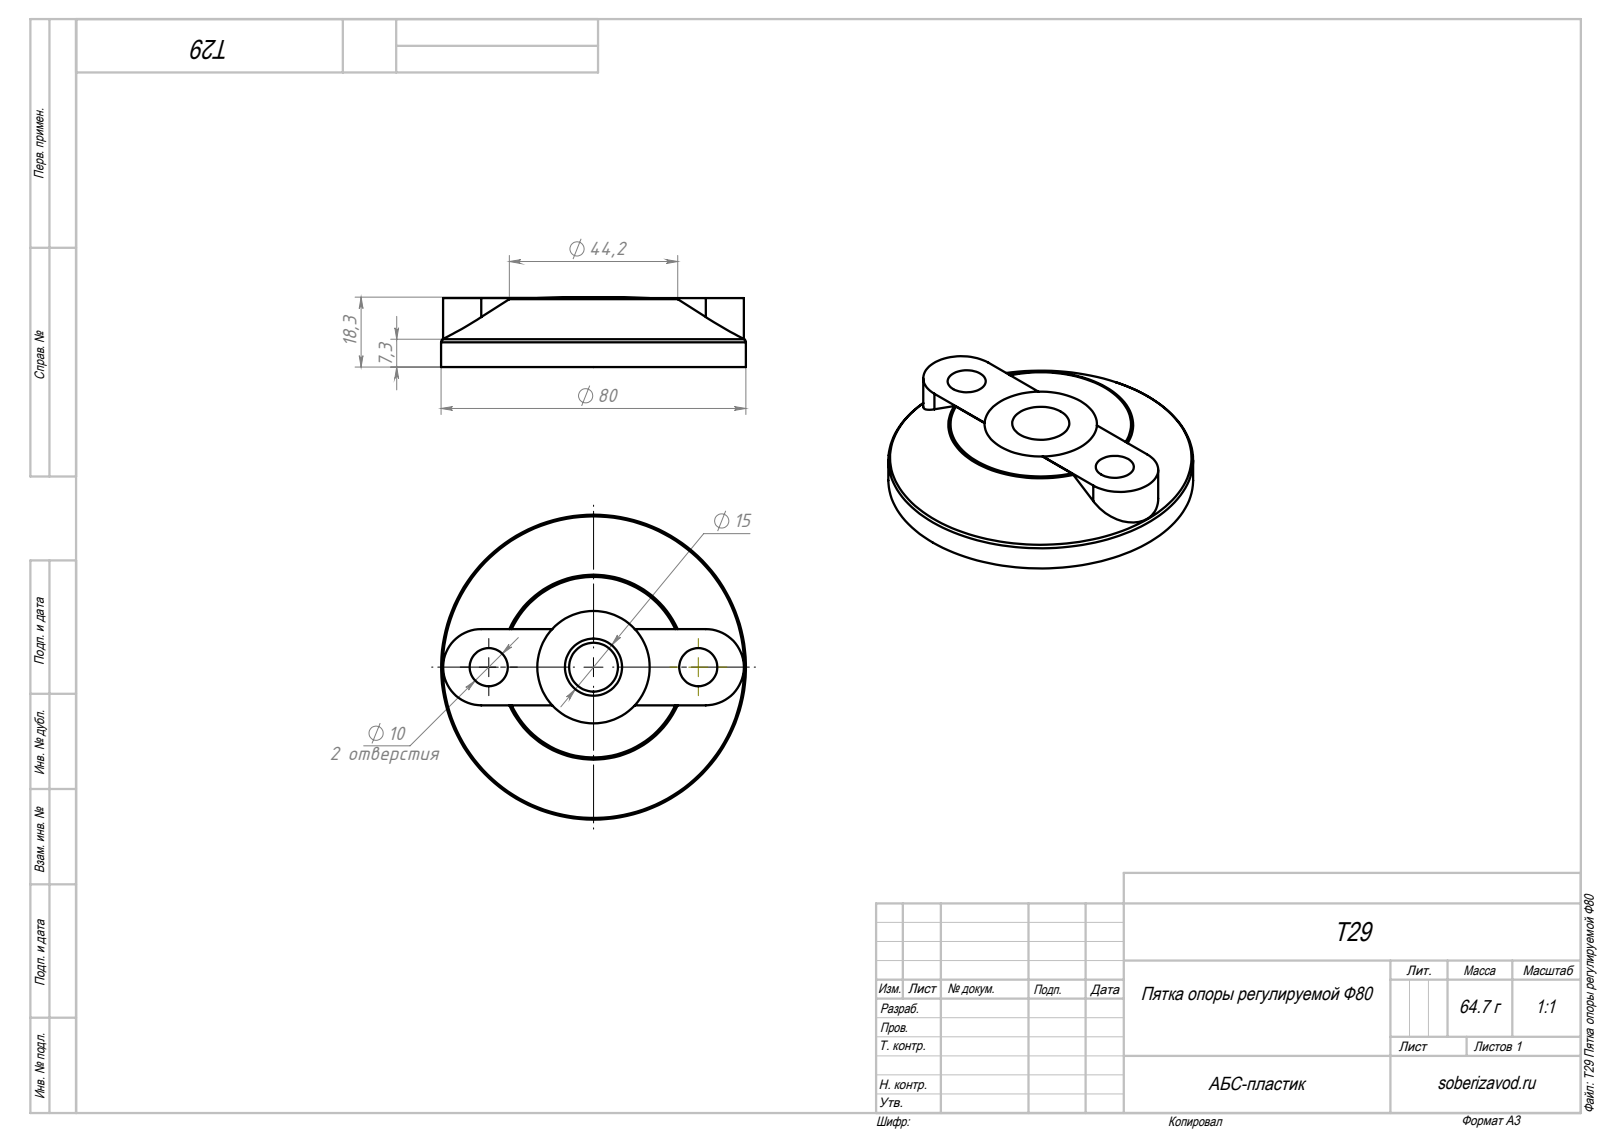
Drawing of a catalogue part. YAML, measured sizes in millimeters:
part_name: "T29 Пятка опоры регулируемой Ф80"
step_written_by: "SolidWorks 2018 (AUTOMOTIVE_DESIGN)"
units: millimeters
bodies: {solids: 1, faces: 37, planar: 12, cylindrical: 14, other: 11}
overall_size: [80, 80, 18.35]
volume: 68462
surface_area: 14844
round_holes:
  - {diameter: 10, count: 2}
  - {diameter: 11, count: 2}
  - {diameter: 15, count: 1}
round_bosses_or_shafts:
  - {diameter: 80, count: 1}
partial_cylinders:
  - {radius: 10, count: 2}
face_to_face_distances: [18.1, 18, 4.1, 13.9, 14, 20, 5, 0.9, 13, 13.1]
hole_center_spacings: [27.5, 55]
